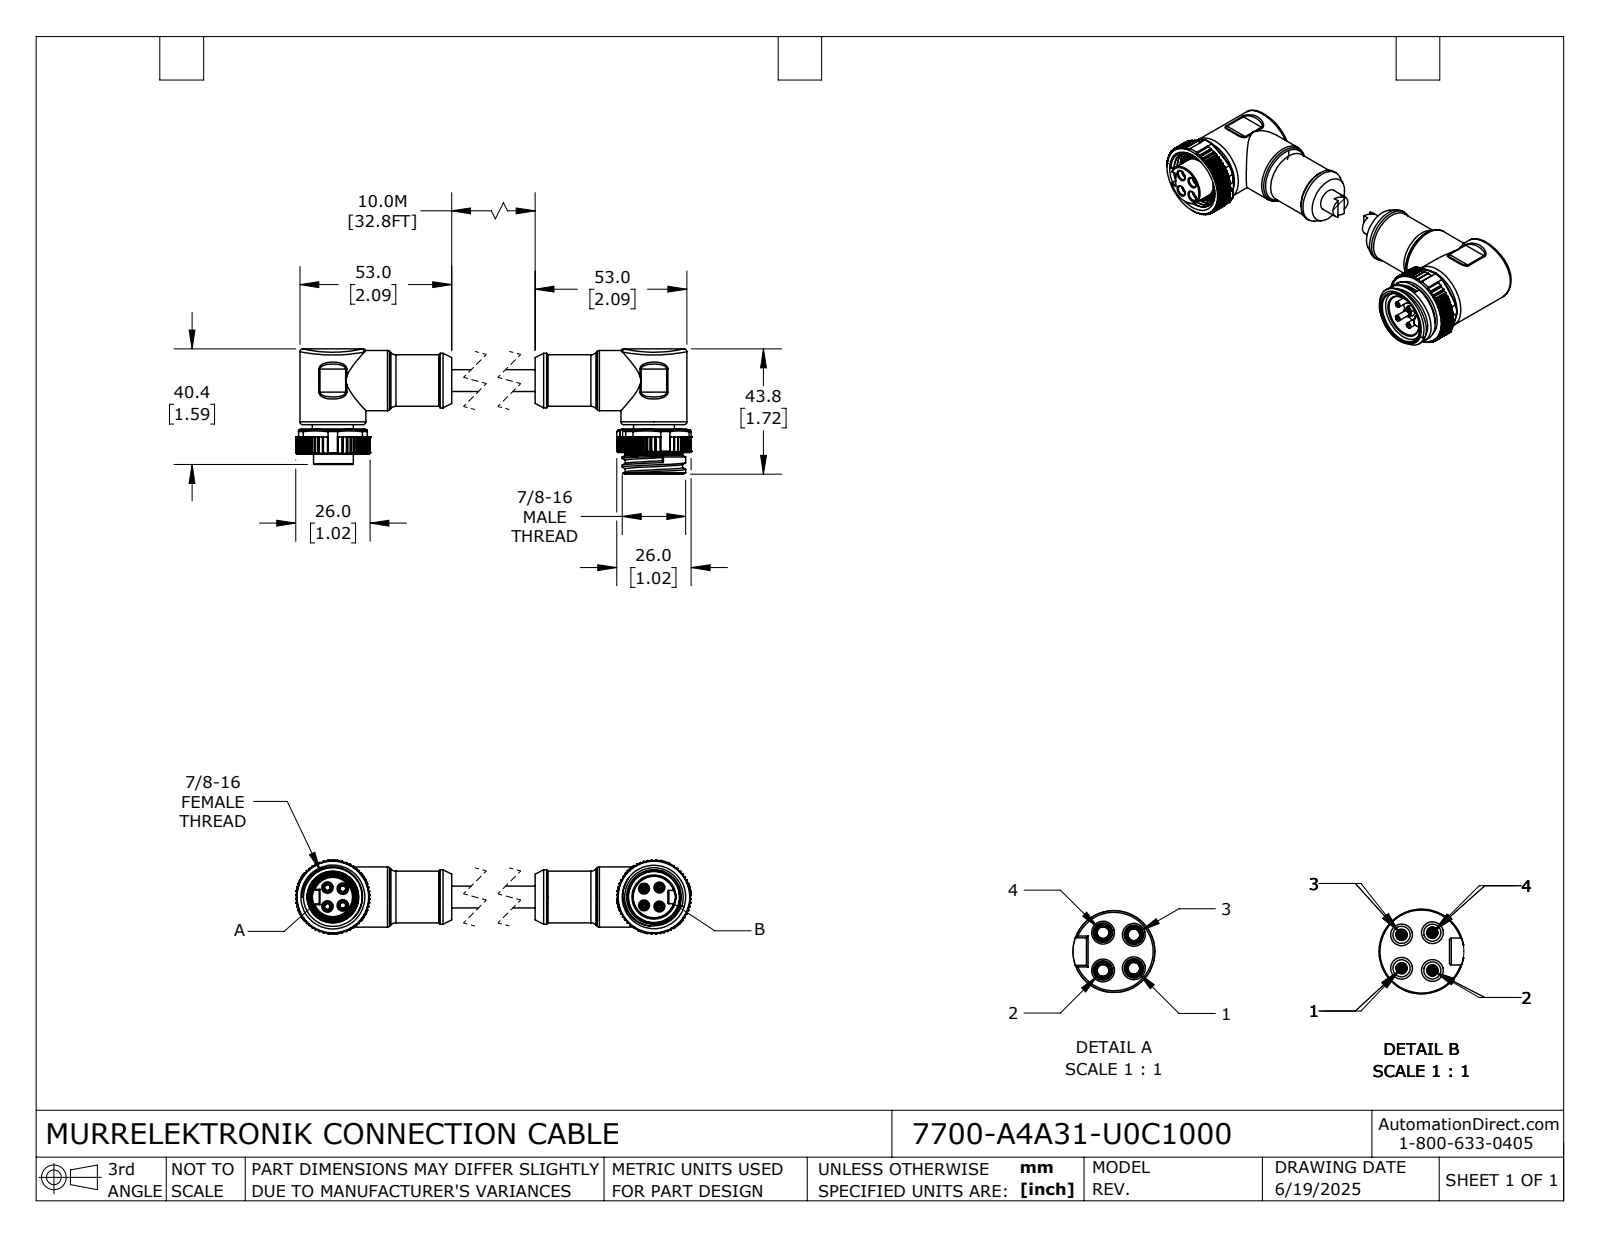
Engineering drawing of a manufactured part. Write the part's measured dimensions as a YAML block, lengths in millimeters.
part_name: "7700-A4A31-U0C1000_MALE; 7700-A4A31-U0C1000_FEMALE; 7700-A4A31-U0C1000"
step_written_by: "SolidWorks 2024 (CONFIG_CONTROL_DESIGN)"
units: millimeters
bodies: {solids: 2, faces: 1268, planar: 520, cylindrical: 581, other: 167}
overall_size: [138.97, 43.76, 26]
volume: 49781
surface_area: 17240
round_holes:
  - {diameter: 2.05, count: 4}
  - {diameter: 3, count: 4}
  - {diameter: 3.4, count: 4}
  - {diameter: 15.6, count: 2}
  - {diameter: 15.5, count: 1}
  - {diameter: 18.5, count: 1}
  - {diameter: 20.5, count: 1}
  - {diameter: 22.22, count: 1}
round_bosses_or_shafts:
  - {diameter: 3, count: 4}
  - {diameter: 2, count: 4}
  - {diameter: 23, count: 2}
  - {diameter: 18.1, count: 2}
  - {diameter: 17.8, count: 2}
  - {diameter: 14.3, count: 2}
  - {diameter: 22.17, count: 1}
  - {diameter: 21, count: 1}
partial_cylinders:
  - {radius: 0.2, count: 252}
  - {radius: 0.3, count: 34}
  - {radius: 0.1, count: 8}
  - {radius: 1, count: 8}
  - {radius: 0.7, count: 4}
  - {radius: 0.73, count: 4}
  - {radius: 2.5, count: 4}
  - {radius: 13, count: 2}
face_to_face_distances: [1.5, 8.8, 7.3, 9.7, 0.9, 7, 30, 8.2, 21, 4.2]
hole_center_spacings: [3.81, 4.54, 5.39, 8.22, 109.56, 114.95, 5.84, 6.6]
